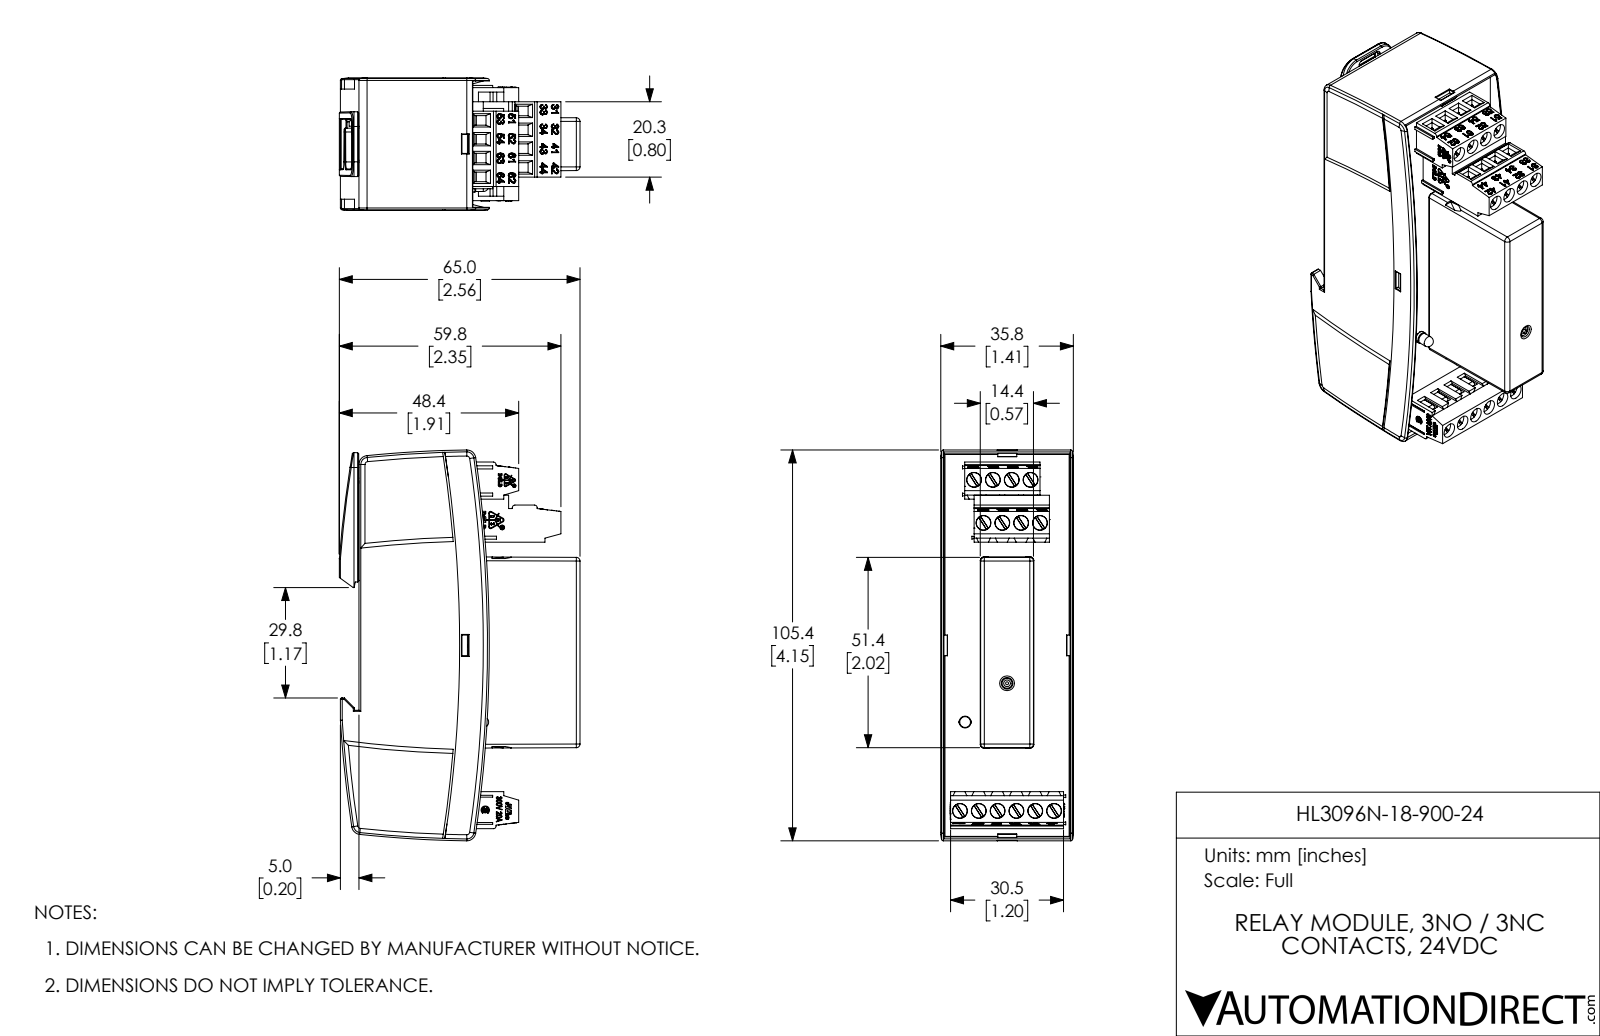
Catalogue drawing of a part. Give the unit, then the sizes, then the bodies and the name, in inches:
Units: inches
Overall size (bounding box): 4.15 × 2.557 × 1.409
Round holes (diameter × count): ⌀0.059 ×27, ⌀0.157 ×14, ⌀0.022 ×2, ⌀0.035 ×2, ⌀0.019 ×1, ⌀0.034 ×1, ⌀0.037 ×1, ⌀0.05 ×1, ⌀0.06 ×1
Round bosses / shafts (diameter × count): ⌀0.154 ×14, ⌀0.019 ×2, ⌀0.126 ×1, ⌀0.114 ×1, ⌀0.046 ×1, ⌀0.037 ×1, ⌀0.034 ×1, ⌀0.031 ×1
Partial cylindrical surfaces — rounded edges, fillets, slot ends (radius × count): R0.006 ×48, R0.02 ×23, R0.008 ×21, R0.012 ×15, R0.039 ×10, R0.004 ×7, R0.005 ×6, R0.005 ×6
Main face-to-face distances: 1.402, 1.154, 0.026, 1.409, 1.394, 1.376, 0.033, 1.368, 1.195, 1.343
Hole centre spacings: 0.394, 0.2, 0.197, 0.44, 0.4, 0.557, 0.467, 0.591
Volume: 8.974 in³ · Surface area: 50.77 in²
Bodies: 1 solid, 3802 faces (2495 planar, 609 cylindrical, 698 other)
Part name (STEP PRODUCT): HL3096N-18-900-24
STEP written by: SolidWorks 2017 (AUTOMOTIVE_DESIGN)
